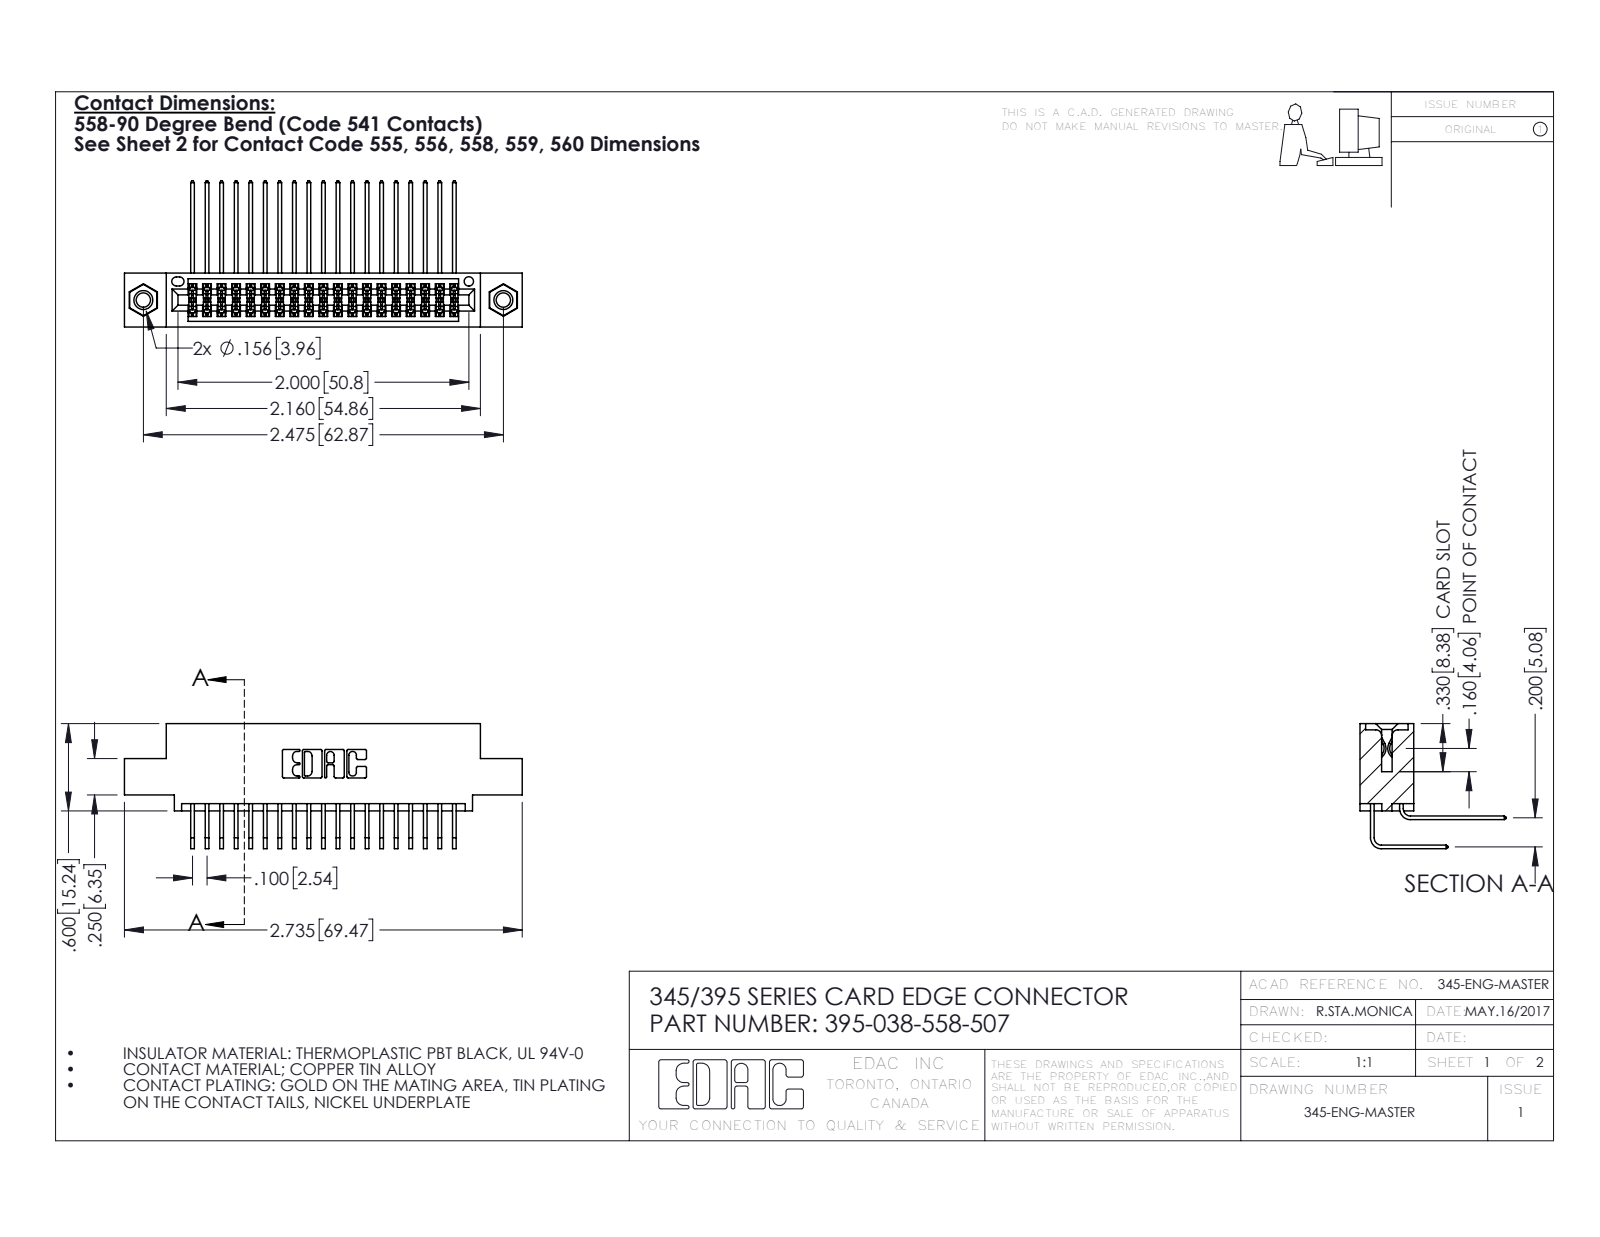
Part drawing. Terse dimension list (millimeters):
name: 345-292-001_558 Tail - 2; 345 Part_0.110 Offset - 0.156 Dia-TI; 395-038-558-507; 345-250-001_345-250-005-103 (+1 more)
written by: SolidWorks 2016 (CONFIG_CONTROL_DESIGN)
unit: mm
bodies: 41 solids, 2166 faces (1446 planar, 704 cylindrical, 16 other)
size: 69.5 × 25.5 × 21.8
volume: 6 670 mm³; area: 10 560 mm²
holes: 2× ⌀2.5, 2× ⌀3.2, 2× ⌀4, 1× ⌀1.6
bosses: 2× ⌀3.9
rounds: 58× R0.2, 22× R0.3, 6× R0.2, 6× R0.8, 3× R0.7, 2× R0.4, 2× R0.5, 2× R0.6
face distances: 5.1, 1.8, 7.6, 9.4, 2.5, 6.9, 0.6, 5.7, 0.6, 4.4
hole spacings: 6.9, 56.9, 62.9
